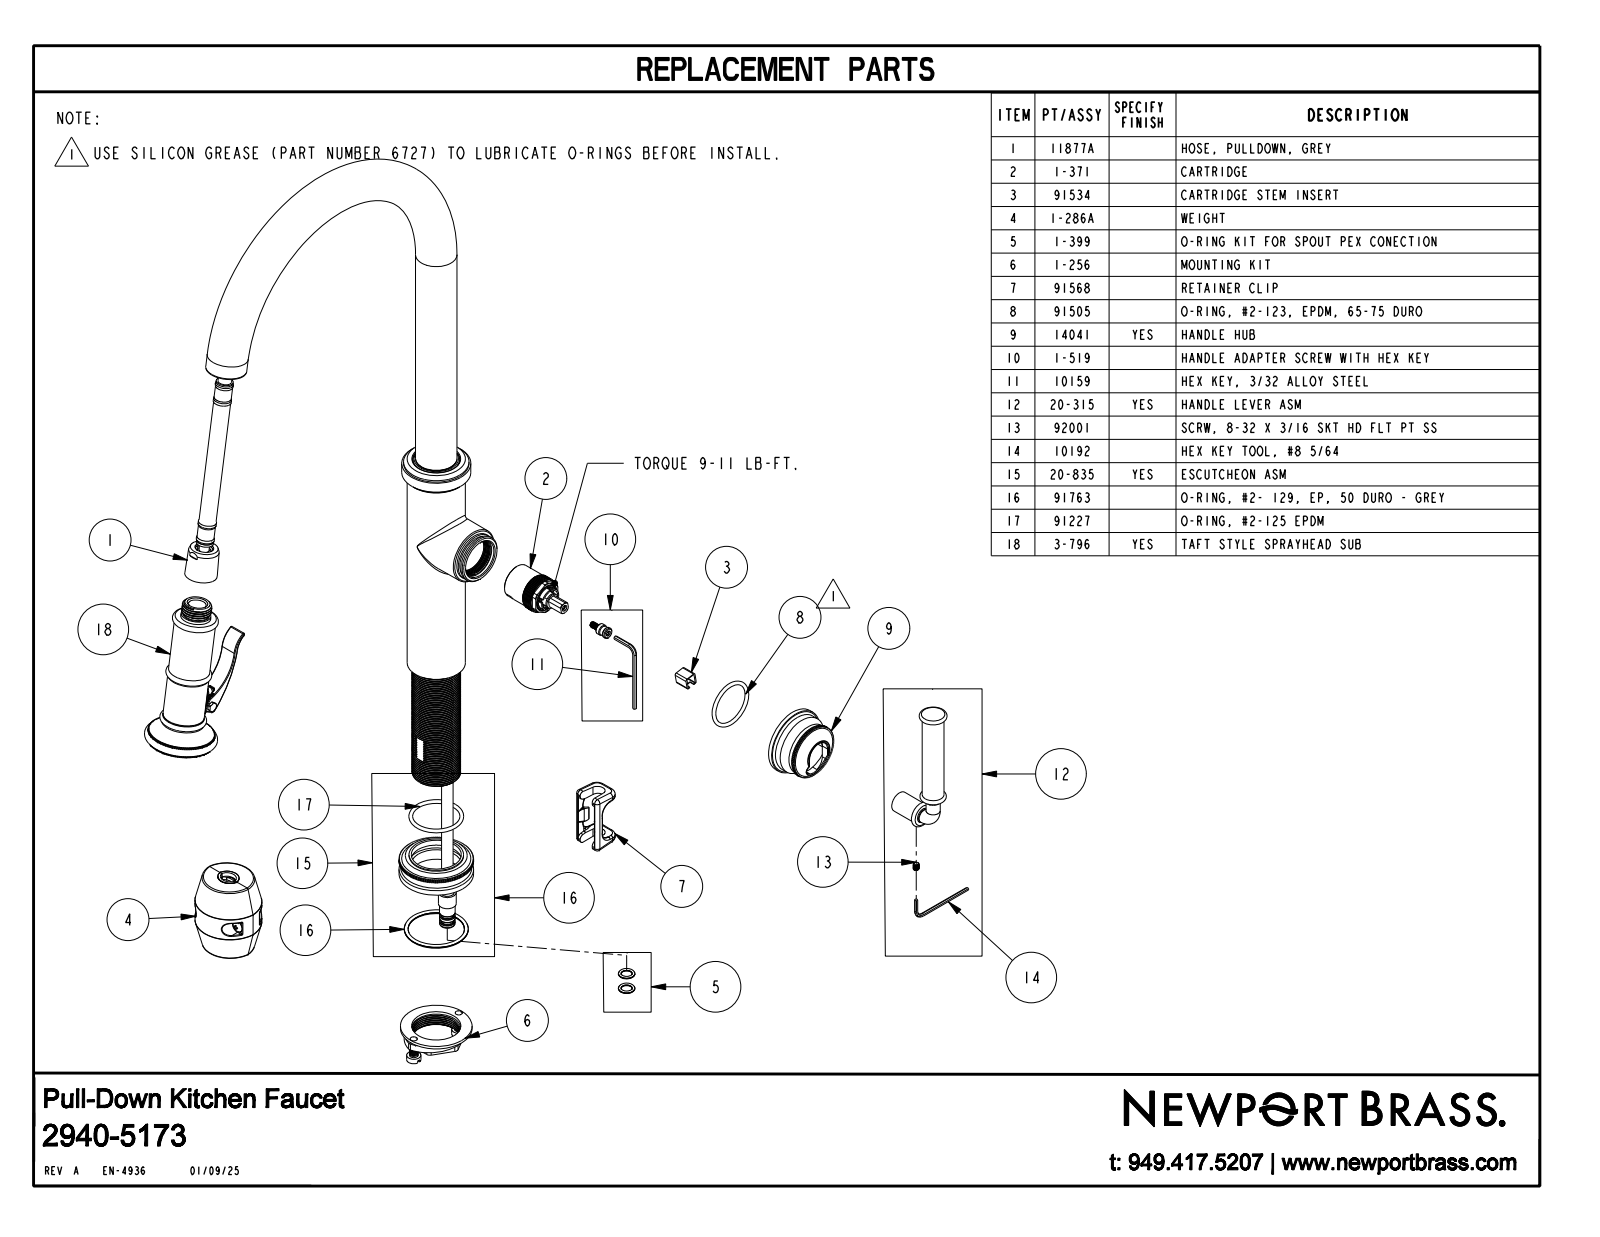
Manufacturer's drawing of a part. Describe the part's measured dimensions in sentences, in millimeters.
The part is named "2940-5173". Its 3-D file was written by "CREO PARAMETRIC BY PTC INC, 2023134 (CONFIG_CONTROL_DESIGN)". It is 1 solid with 2978 faces: 1766 planar, 659 cylindrical and 553 other. Overall it measures 482 by 273.4 by 121.6 millimeters. Its volume is 738 600 cubic millimeters and its surface area 103 900 square millimeters. Round holes: 18 of diameter 1, 1 of diameter 4.3, 1 of diameter 5.3, 1 of diameter 10.2, 1 of diameter 12, 1 of diameter 33. Round bosses or shafts: 18 of diameter 2.6, 2 of diameter 29, 2 of diameter 9.9, 1 of diameter 52.1, 1 of diameter 50.8, 1 of diameter 49.5, 1 of diameter 48.3, 1 of diameter 47.6. Partial cylindrical surfaces (rounded edges, fillets, slot ends): 21 of radius 0.8, 16 of radius 0.5, 14 of radius 1.7, 7 of radius 0.6, 5 of radius 1.5, 4 of radius 1.1, 2 of radius 9, 1 of radius 1. The main face-to-face distances are 2.5, 189.7, 162.8, 165.4, 13, 176.8, 175.8, 14, 11.4, 42. The hole center spacings are 9.3, 16.2, 17.6, 12, 3.3, 6.4, 14.3, 18.4.
